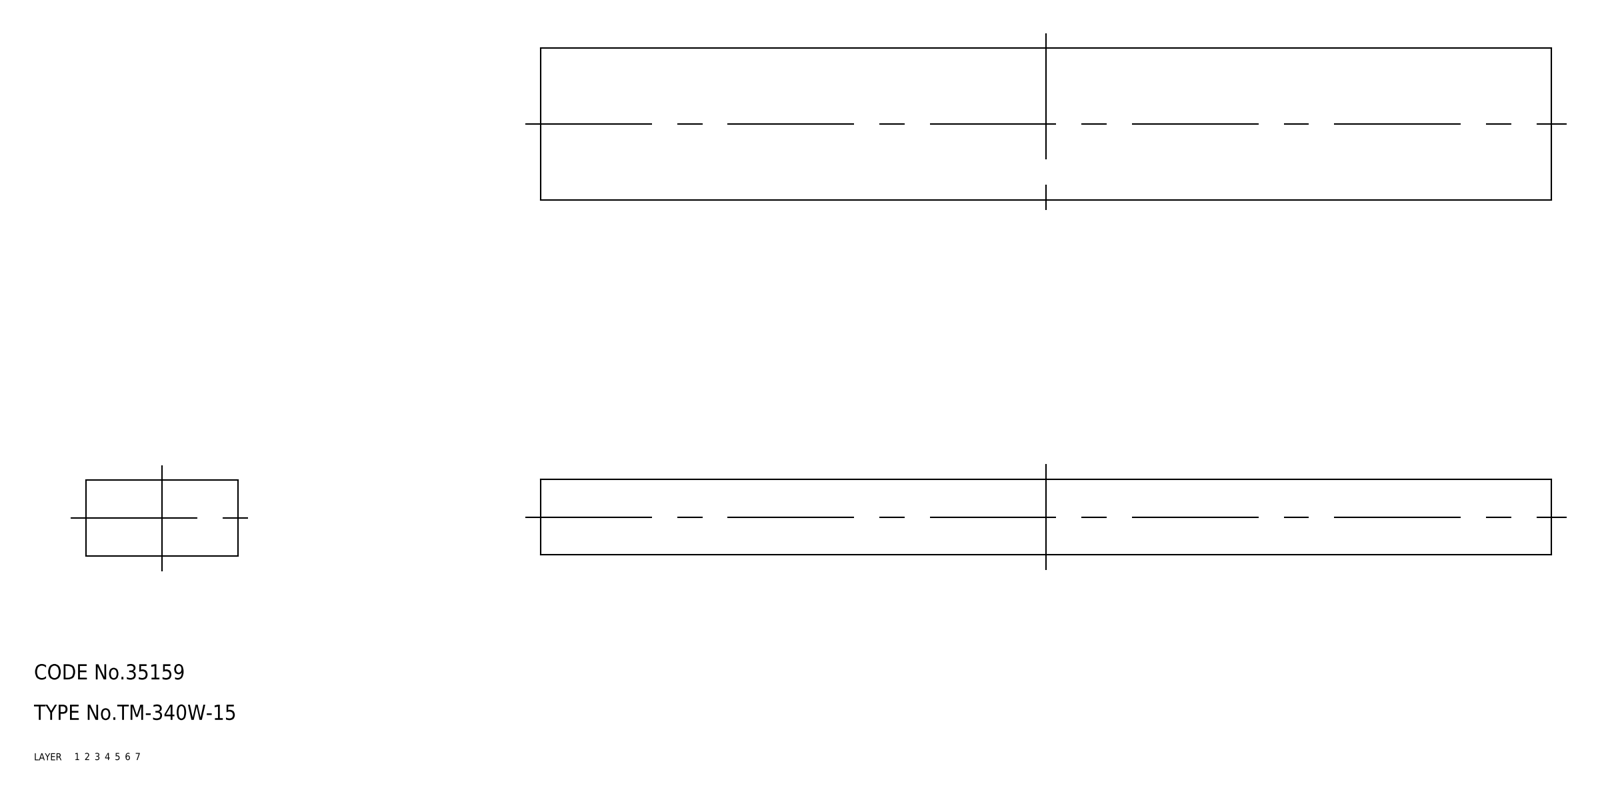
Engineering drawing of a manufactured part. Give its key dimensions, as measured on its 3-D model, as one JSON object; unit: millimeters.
{"part_name": "rubber foam; TM_340W_15", "step_written_by": "SolidWorks 2015 (AUTOMOTIVE_DESIGN)", "units": "millimeters", "bodies": {"solids": 1, "faces": 6, "planar": 6, "cylindrical": 0, "other": 0}, "overall_size": [200, 30, 15], "volume_mm3": 90000, "surface_area_mm2": 18900, "face_to_face_distances": [15, 30, 200]}
